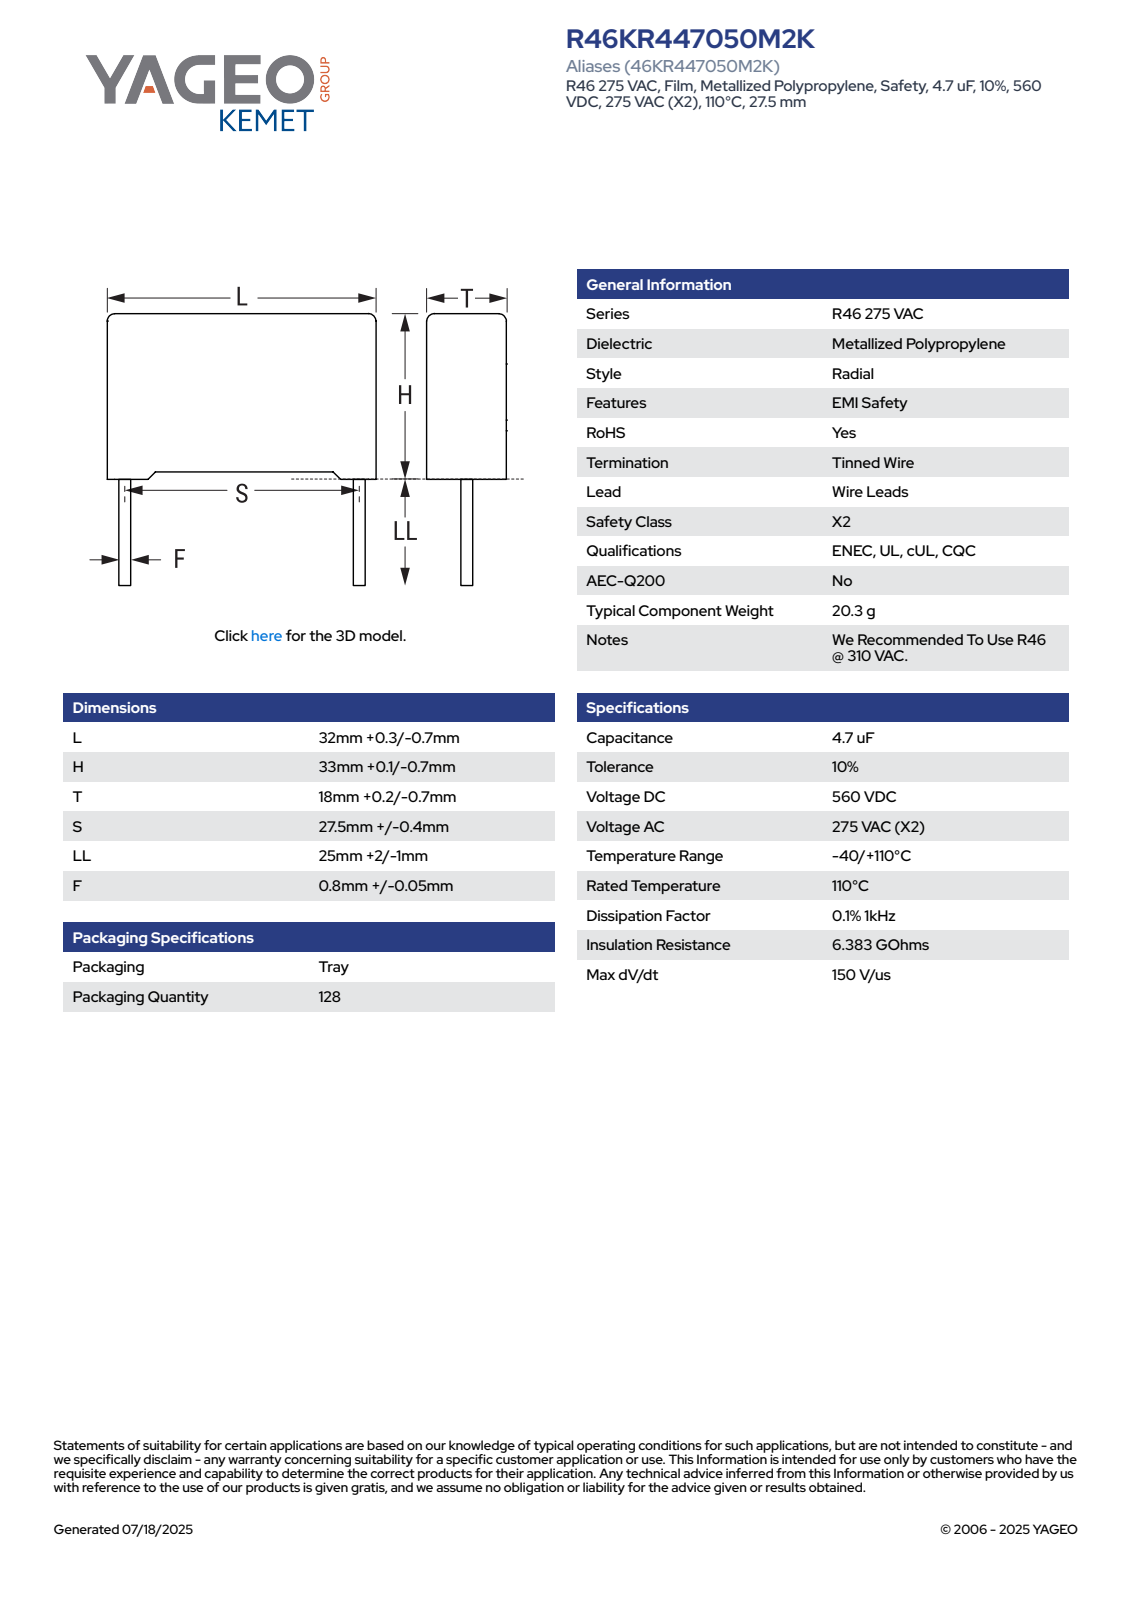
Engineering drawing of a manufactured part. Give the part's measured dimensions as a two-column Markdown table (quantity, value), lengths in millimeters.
| quantity | value |
| --- | --- |
| part name | CFR_RB2_32X33X18_L32.3H33.1T18.2S27.5LL27F0.85 |
| STEP written by | SolidWorks 2021 (AUTOMOTIVE_DESIGN) |
| units | millimeters |
| bodies | 4 solids, 85 faces (77 planar, 8 cylindrical, 0 other) |
| overall size | 60.1 × 32.3 × 18.2 |
| volume | 18 919 mm³ |
| surface area | 4 711 mm² |
| round bosses / shafts (diameter × count) | 0.85 × 2 |
| partial cylindrical surfaces (radius × count) | 0.5 × 4 |
| main face-to-face distances | 18.2, 32.3, 31.96, 0.39, 32.35, 0.75, 1.14, 33.1, 1.08, 31.22 |
